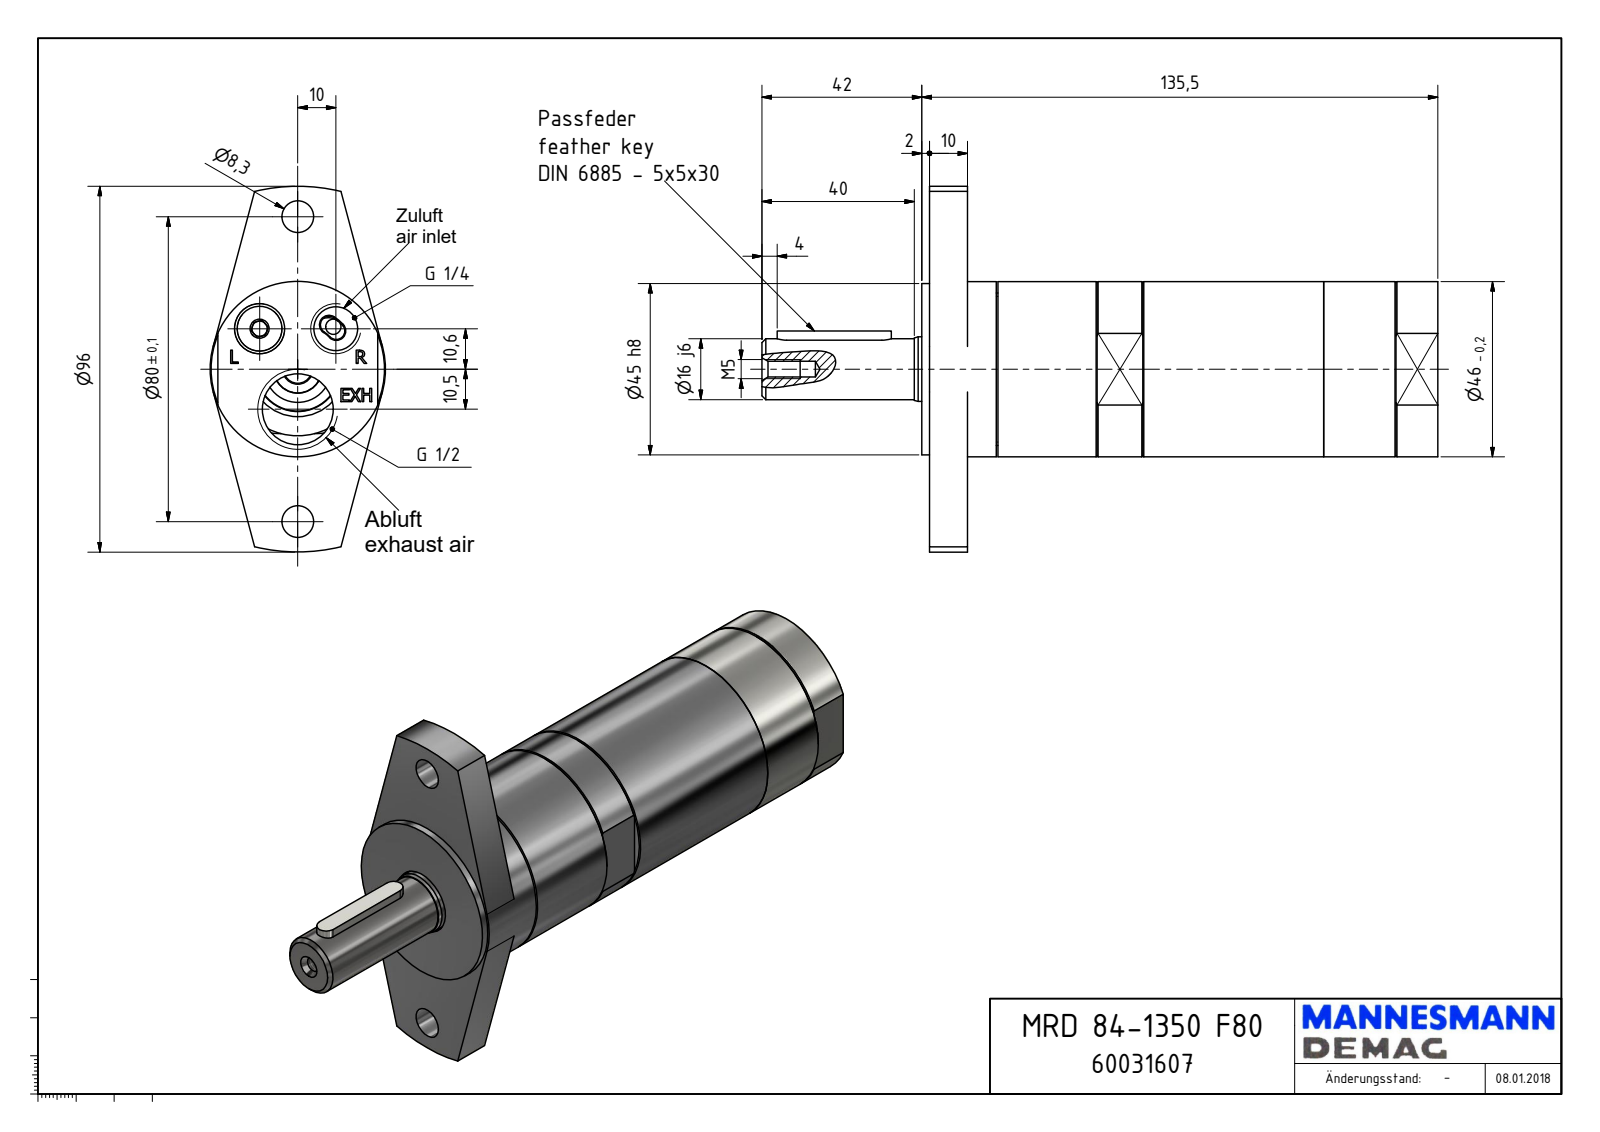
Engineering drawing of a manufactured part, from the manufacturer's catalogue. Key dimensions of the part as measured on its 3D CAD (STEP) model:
Part name (STEP PRODUCT): MRD 84-1350 F80_60032607
STEP written by: Autodesk Inventor 2018 (AUTOMOTIVE_DESIGN)
Units: millimetres
Bodies: 1 solid, 165 faces (108 planar, 31 cylindrical, 26 other)
Overall size (bounding box): 177.5 × 96 × 46
Volume: 243 690 mm³ · Surface area: 32 852 mm²
Round holes (diameter × count): ⌀8.3 ×2, ⌀4 ×1, ⌀4.13 ×1, ⌀11.45 ×1, ⌀17.5 ×1, ⌀18.63 ×1
Round bosses / shafts (diameter × count): ⌀46 ×1, ⌀45 ×1, ⌀40 ×1, ⌀33.93 ×1, ⌀16.95 ×1, ⌀16 ×1
Partial cylindrical surfaces — rounded edges, fillets, slot ends (radius × count): R2.5 ×2, R5 ×2, R5.72 ×1, R19 ×1, R48 ×1
Main face-to-face distances: 10, 12, 2, 123.5, 135.5, 133.5, 42, 8, 115.5, 46
Hole centre spacings: 14.57, 23.35, 31.05, 40, 51.58, 10.5, 20, 29.5
